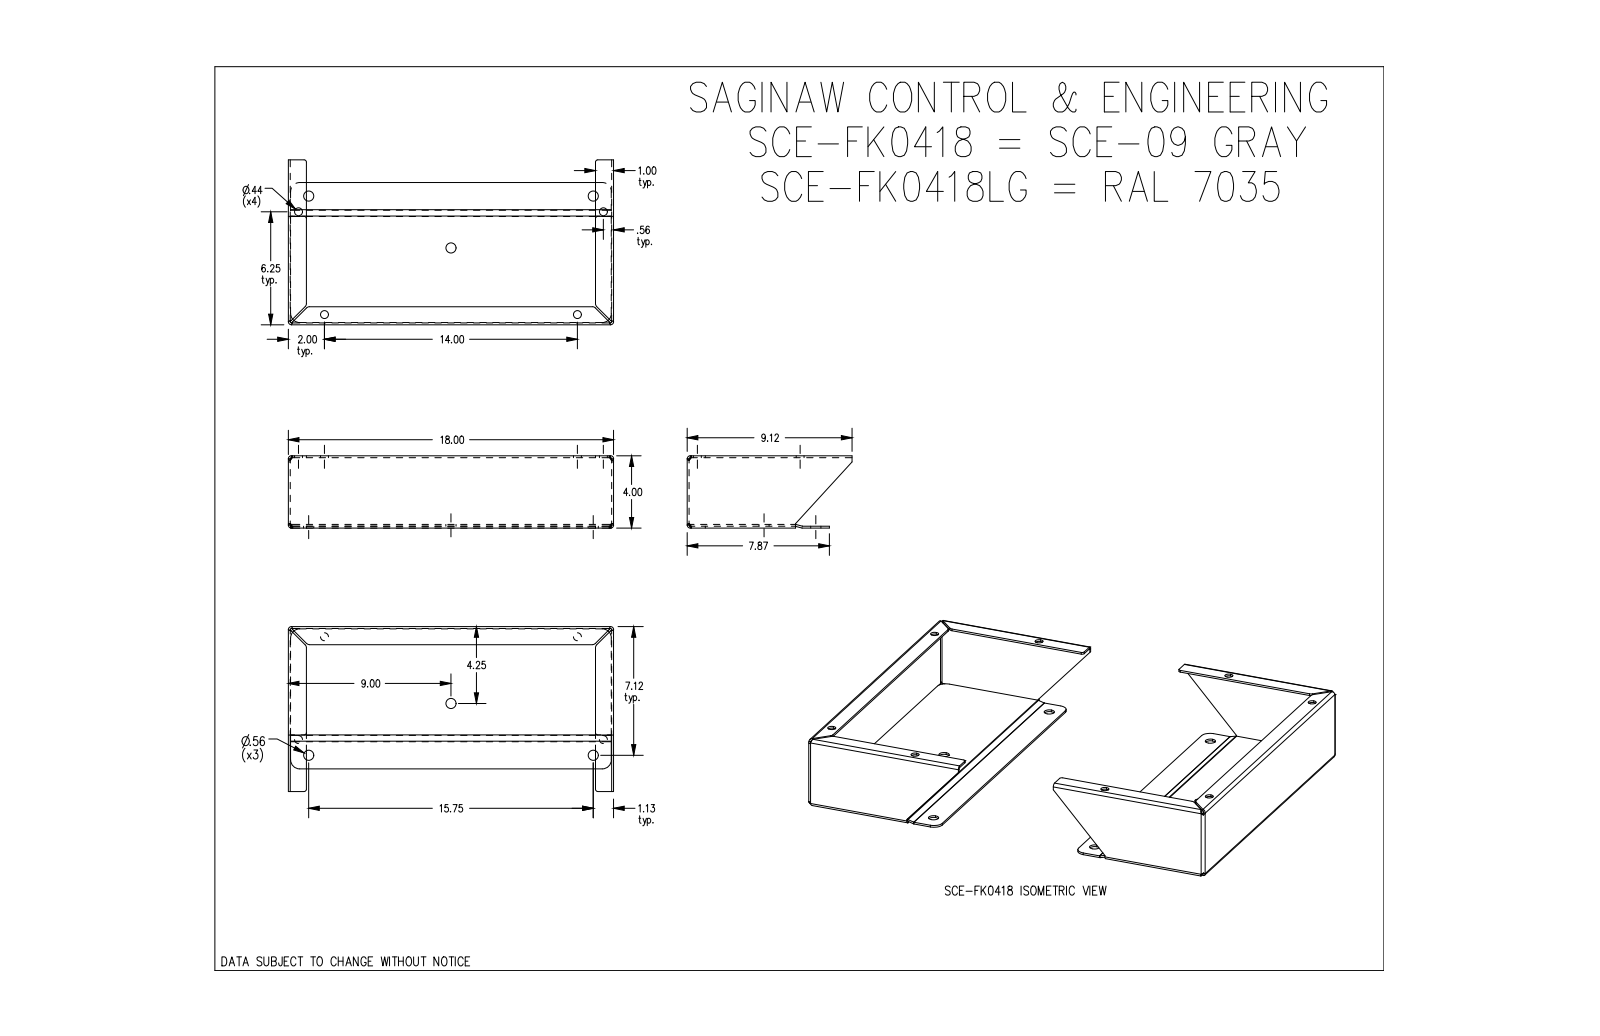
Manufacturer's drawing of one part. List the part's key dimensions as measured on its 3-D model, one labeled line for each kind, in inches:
Part name (STEP PRODUCT): SCE-FK0418
STEP written by: SolidWorks 2019 (CONFIG_CONTROL_DESIGN)
Units: inches
Bodies: 4 solids, 214 faces (96 planar, 86 cylindrical, 32 other)
Overall size (bounding box): 24 × 18 × 4
Volume: 66.37 in³ · Surface area: 1 306 in²
Round holes (diameter × count): ⌀0.437 ×8, ⌀0.563 ×6
Partial cylindrical surfaces — rounded edges, fillets, slot ends (radius × count): R0.166 ×16, R0.062 ×12, R0.125 ×8, R0.22 ×8, R0.5 ×8, R0.063 ×6
Main face-to-face distances: 0.104, 23.896, 3.792, 17.896, 0.101, 3.893, 3.896, 24, 23.792, 18
Hole centre spacings: 1.035, 5.866, 6.614, 7.913, 8.671, 10.646, 14.884, 15.919
